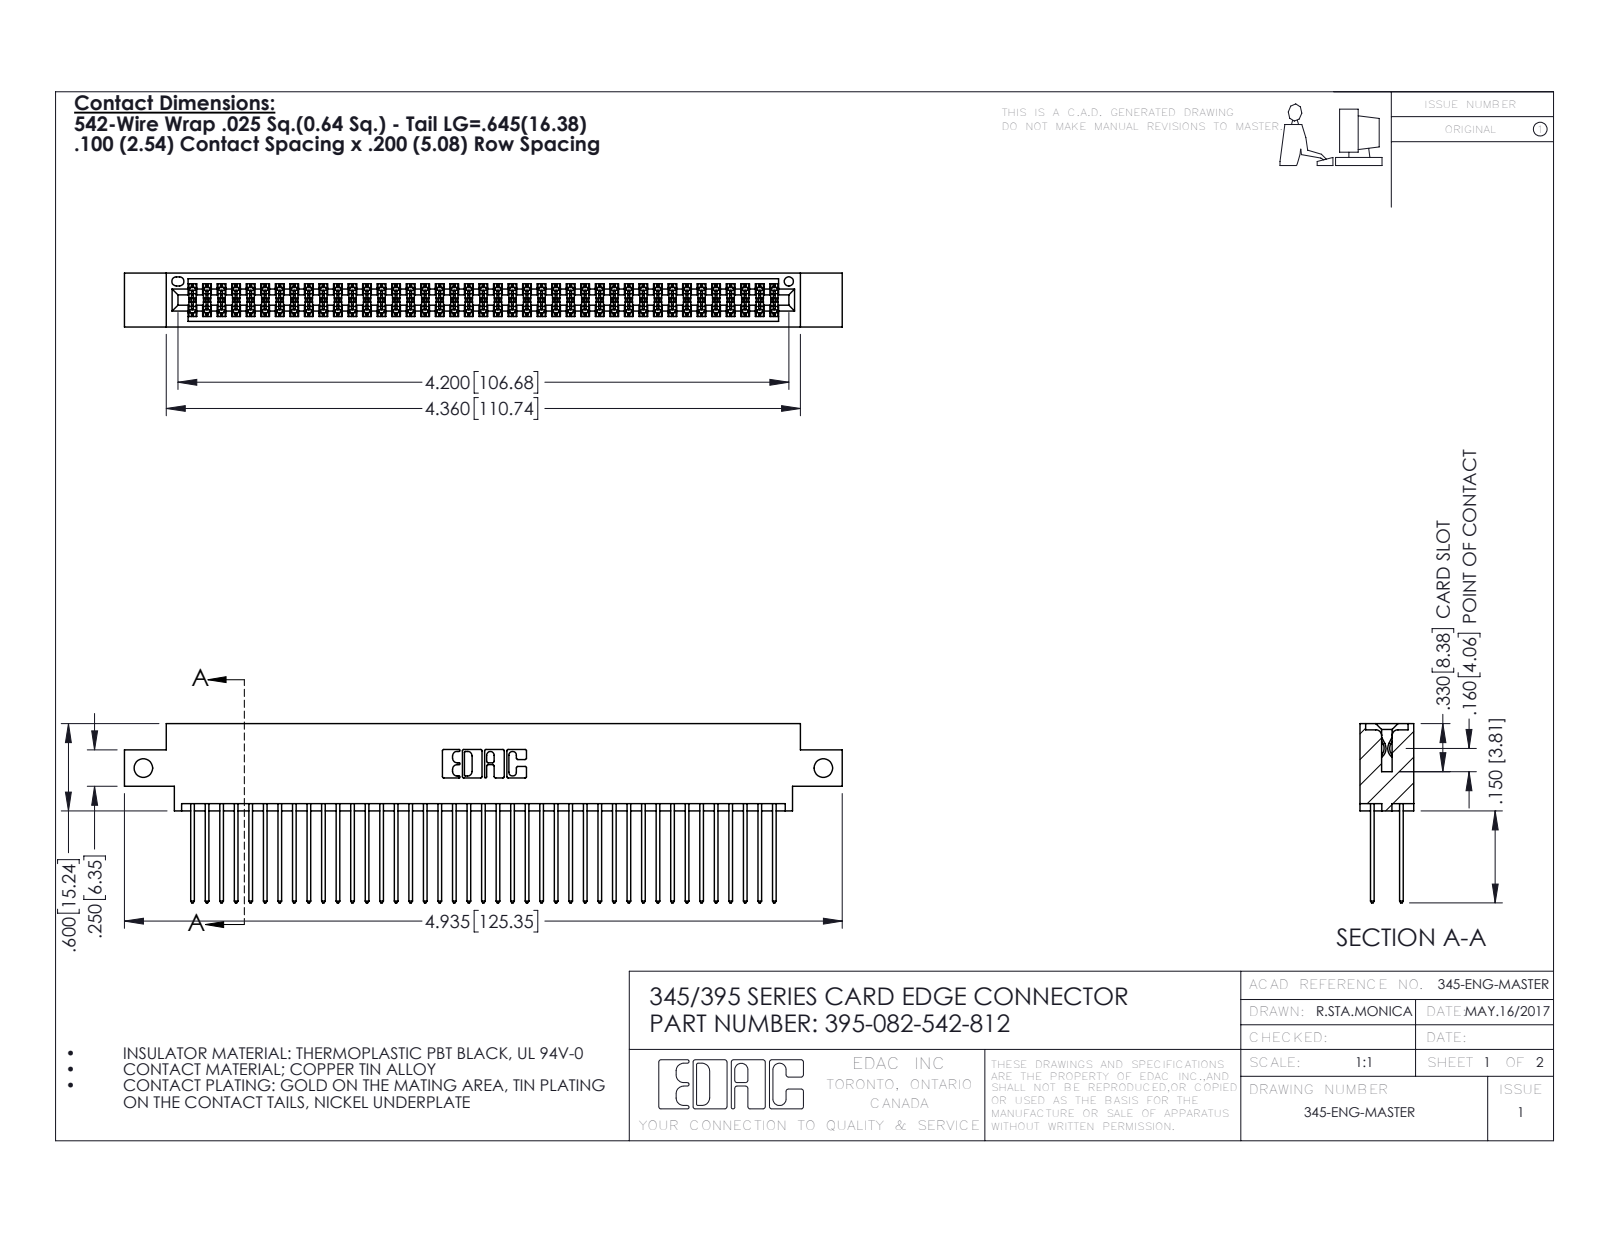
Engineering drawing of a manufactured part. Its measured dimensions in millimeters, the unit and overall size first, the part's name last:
Units: millimetres
Overall size (bounding box): 125.3 × 31.3 × 9.4
Round holes (diameter × count): ⌀3.3 ×2, ⌀1.6 ×1
Partial cylindrical surfaces — rounded edges, fillets, slot ends (radius × count): R0.2 ×123, R0.3 ×82, R0.3 ×22, R0.2 ×6, R0.8 ×6, R0.7 ×3, R0.4 ×2, R0.5 ×2
Main face-to-face distances: 7.6, 1.8, 5.1, 2.5, 6.9, 0.6, 9.4, 5.7, 4.4, 3.8
Hole centre spacings: 118.7
Volume: 12 400 mm³ · Surface area: 20 030 mm²
Bodies: 83 solids, 4230 faces (2790 planar, 1440 cylindrical, 0 other)
Part name (STEP PRODUCT): 395-082-542-812; 345-292-001_345-293-142; 345 Part_0.170 Offset - Side Mount
STEP written by: SolidWorks 2016 (CONFIG_CONTROL_DESIGN)
